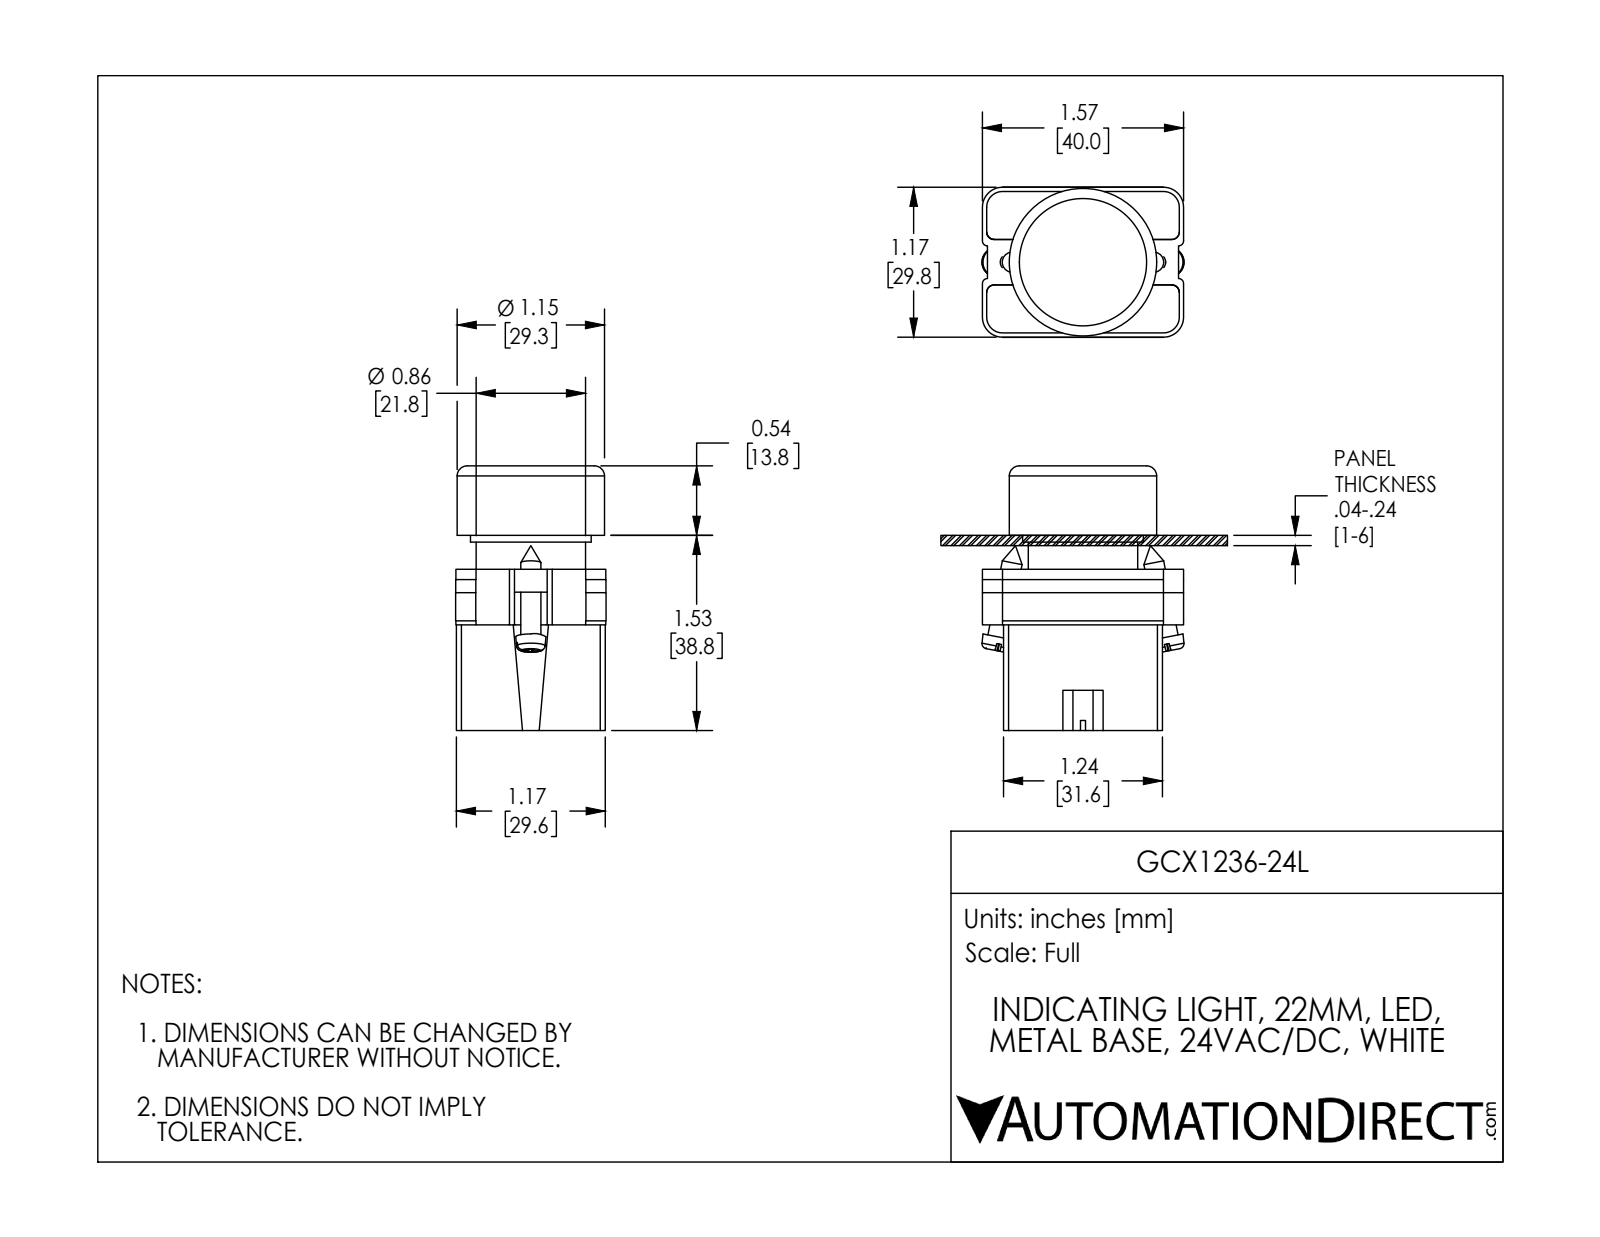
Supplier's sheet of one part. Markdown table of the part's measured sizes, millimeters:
| quantity | value |
| --- | --- |
| part name | ecx1029; ECX1050; GCX1236L OPERATOR; GCX1236-24L |
| STEP written by | SolidWorks 2016 (AUTOMOTIVE_DESIGN) |
| units | millimeters |
| bodies | 7 solids, 339 faces (178 planar, 134 cylindrical, 27 other) |
| overall size | 52.6 × 40.2 × 29.9 |
| volume | 37 170 mm³ |
| surface area | 20 120 mm² |
| round holes (diameter × count) | 3.1 × 2, 3.3 × 2, 5 × 1, 11.9 × 1, 21.6 × 1, 22.3 × 1, 22.6 × 1, 28 × 1 |
| round bosses / shafts (diameter × count) | 4 × 4, 29.3 × 1, 27.7 × 1, 24 × 1, 21.7 × 1, 19.8 × 1, 12.8 × 1 |
| partial cylindrical surfaces (radius × count) | 1.5 × 24, 1 × 12, 3.1 × 12, 4 × 12, 1 × 8, 3.3 × 2, 10 × 1, 10.1 × 1 |
| main face-to-face distances | 21.8, 31.6, 21, 42.8, 28.9, 0.8, 49.9, 7, 0.8, 29.6 |
